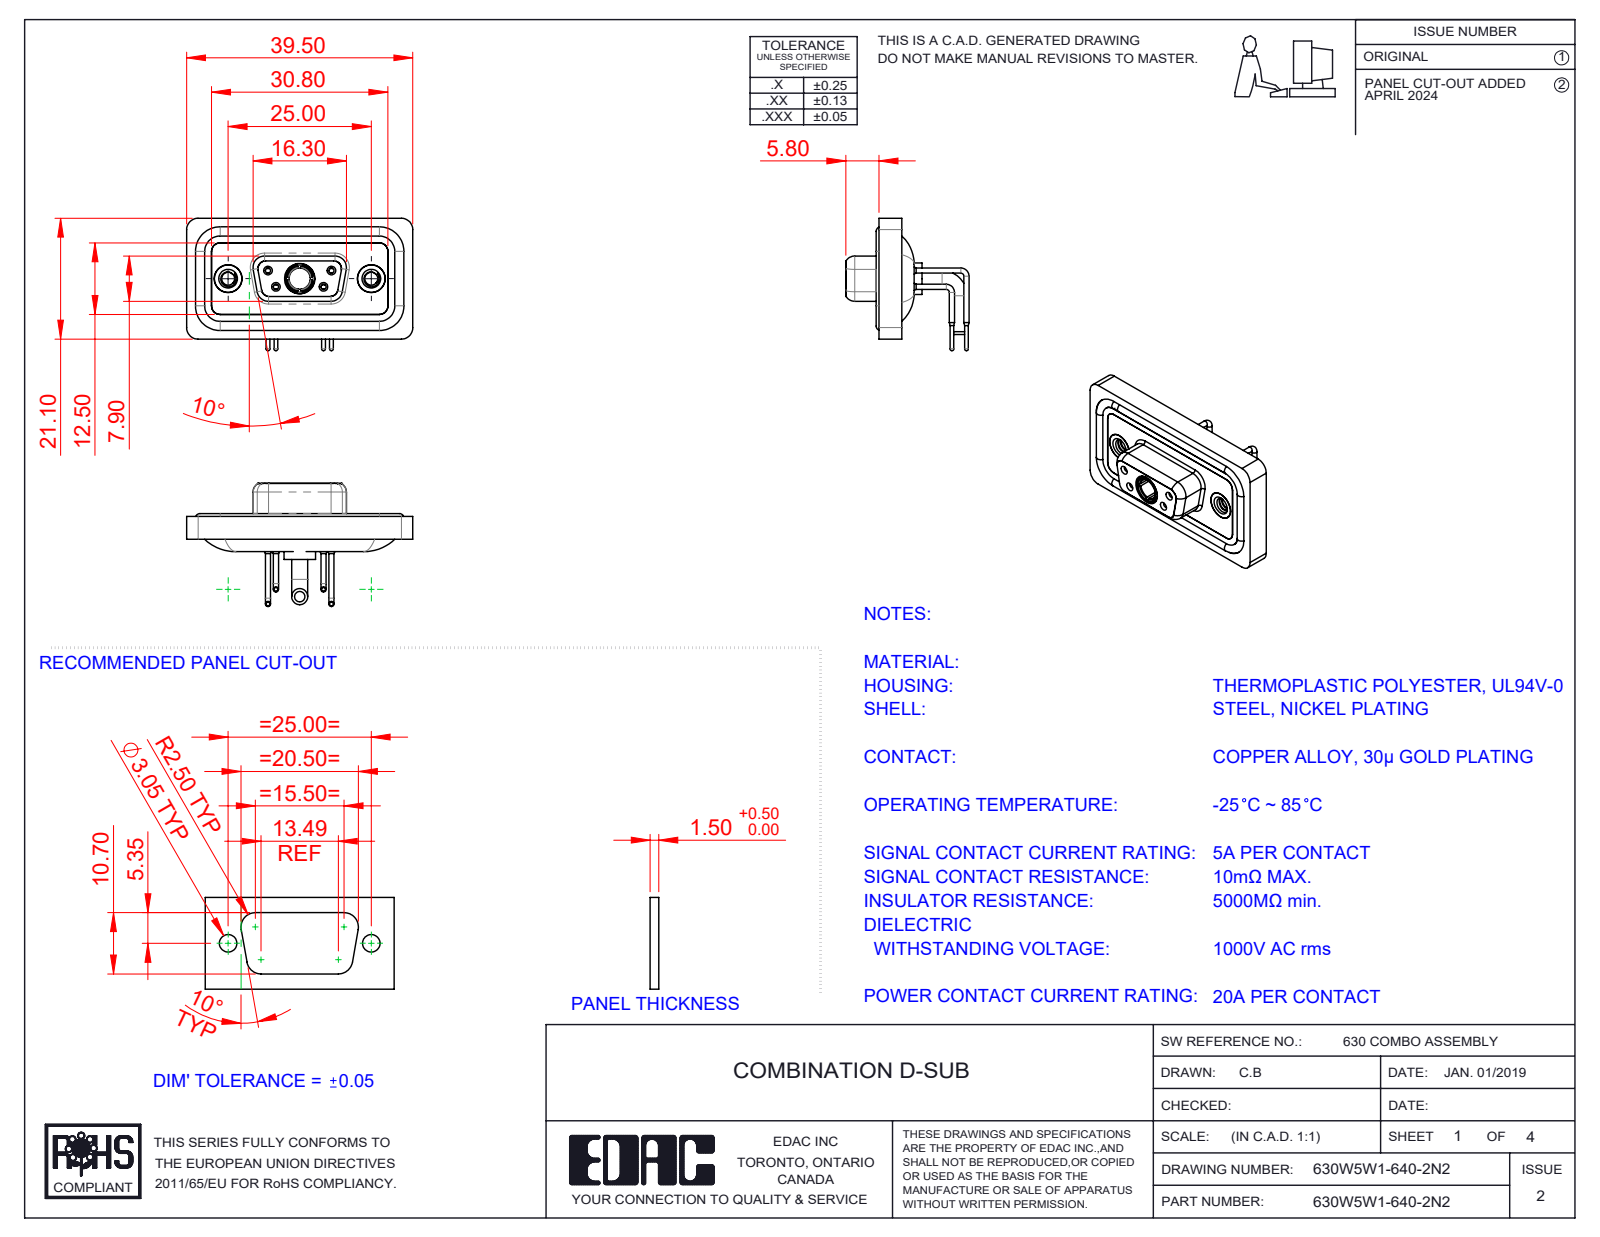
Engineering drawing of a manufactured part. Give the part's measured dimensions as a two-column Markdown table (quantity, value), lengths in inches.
| quantity | value |
| --- | --- |
| part name | Power Socket_20A RA; 630Combo Housing_5W1; 630Combo Threaded Rivet_2; 630Combo Contact Row 1_50 Contacts (+5 more) |
| STEP written by | SolidWorks 2023 (CONFIG_CONTROL_DESIGN) |
| units | inches |
| bodies | 13 solids, 676 faces (194 planar, 305 cylindrical, 177 other) |
| overall size | 1.555 × 0.91 × 0.848 |
| volume | 0.295 in³ |
| surface area | 12.16 in² |
| round holes (diameter × count) | 0.035 × 4, 0.043 × 4, 0.059 × 4, 0.079 × 4, 0.191 × 3, 0.063 × 2, 0.067 × 2, 0.089 × 2, 0.157 × 2, 0.159 × 2, 0.197 × 2, 0.146 × 1 |
| round bosses / shafts (diameter × count) | 0.063 × 6, 0.035 × 4, 0.026 × 4, 0.195 × 2, 0.189 × 2, 0.11 × 2, 0.217 × 1, 0.205 × 1 |
| partial cylindrical surfaces (radius × count) | 0.059 × 18, 0.079 × 18, 0.053 × 8, 0.063 × 8, 0.01 × 4, 0.02 × 4, 0.024 × 4, 0.026 × 4 |
| main face-to-face distances | 0.016, 0.071, 0.043, 0.114, 0.098, 0.063, 0.122, 0.083, 0.059, 0.02 |
| hole center spacings | 0.124, 0.225, 0.28, 0.492, 0.713, 0.173, 0.173, 0.327 |
